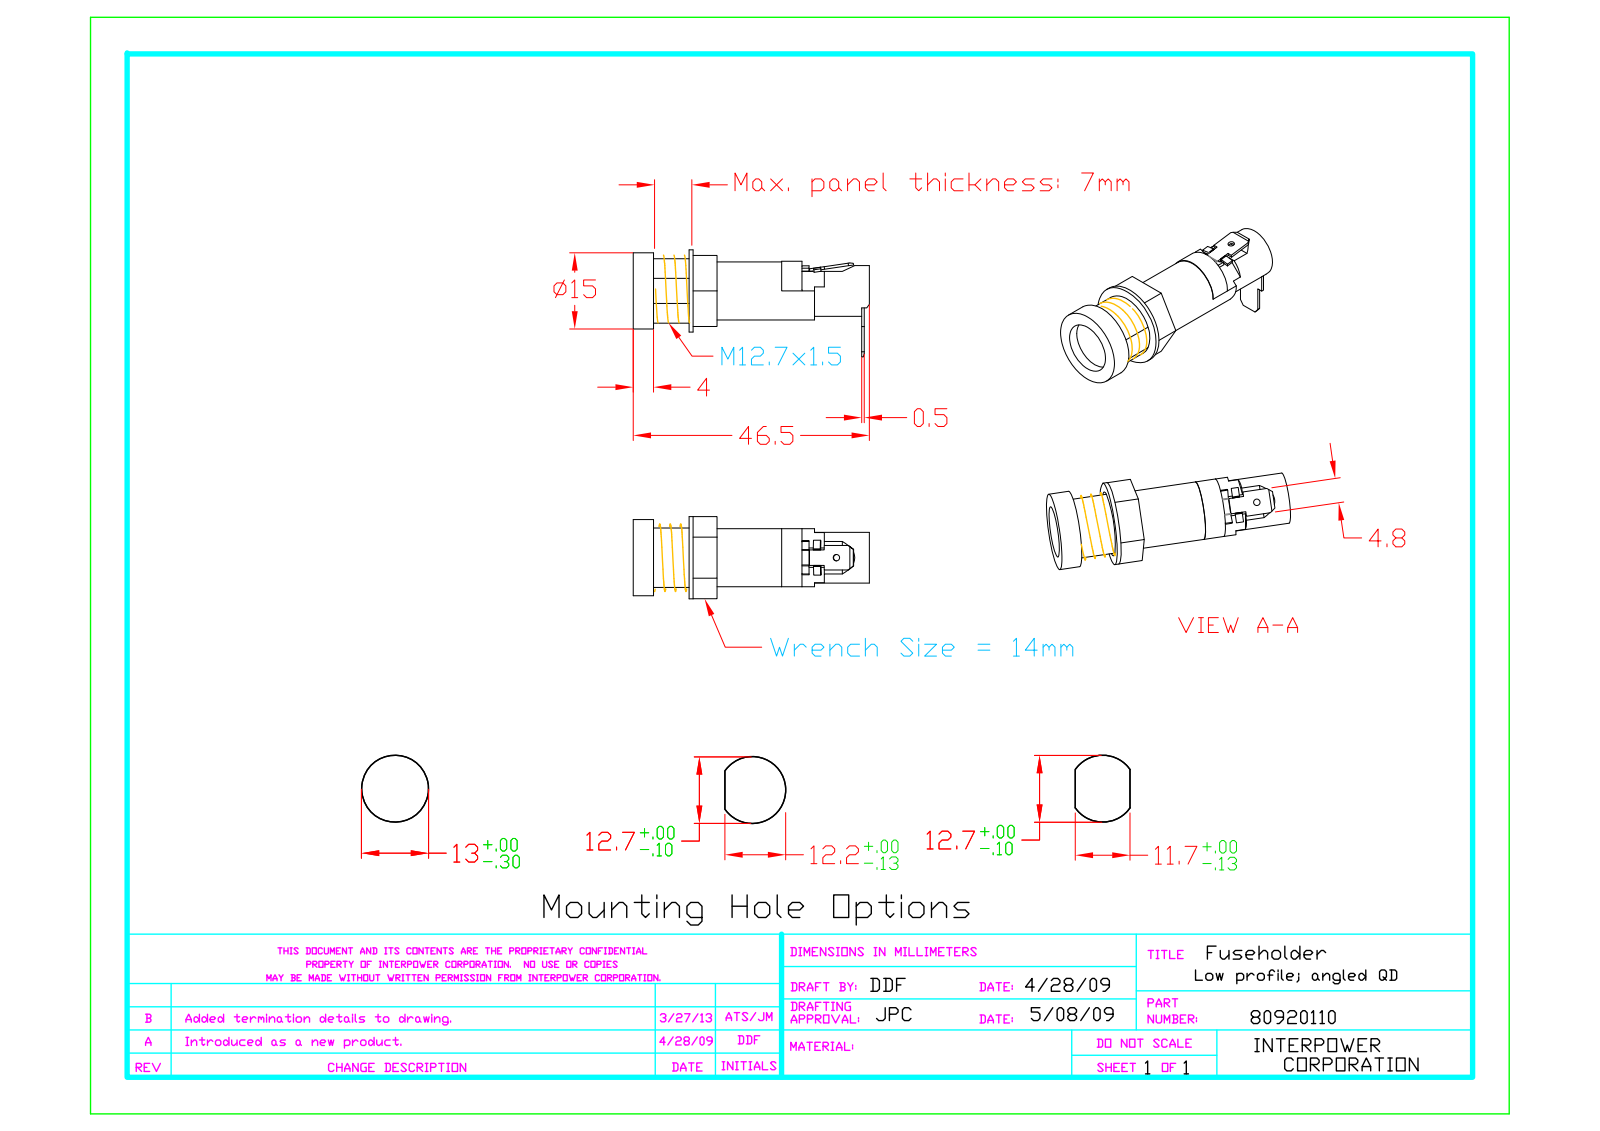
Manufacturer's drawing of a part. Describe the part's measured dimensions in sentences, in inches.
The part is named "80920110". Its 3-D file was written by "SolidWorks 2012 (AUTOMOTIVE_DESIGN)". It is 5 solids with 146 faces: 104 planar, 37 cylindrical and 5 other. Overall it measures 1.831 by 0.83 by 0.638 inches. Its volume is 0.308 cubic inches and its surface area 4.377 square inches. Round holes: 2 of diameter 0.05, 1 of diameter 0.15, 1 of diameter 0.394, 1 of diameter 0.5. Round bosses or shafts: 1 of diameter 0.638, 1 of diameter 0.591, 1 of diameter 0.45, 1 of diameter 0.437. Partial cylindrical surfaces (rounded edges, fillets, slot ends): 5 of radius 0.02, 5 of radius 0.04, 1 of radius 0.139, 1 of radius 0.147, 1 of radius 0.225. The main face-to-face distances are 0.551, 0.079, 0.02, 1.772, 1.792, 1.359, 1.339, 0.433, 1.713, 1.693. The hole center spacings are 0.383.
